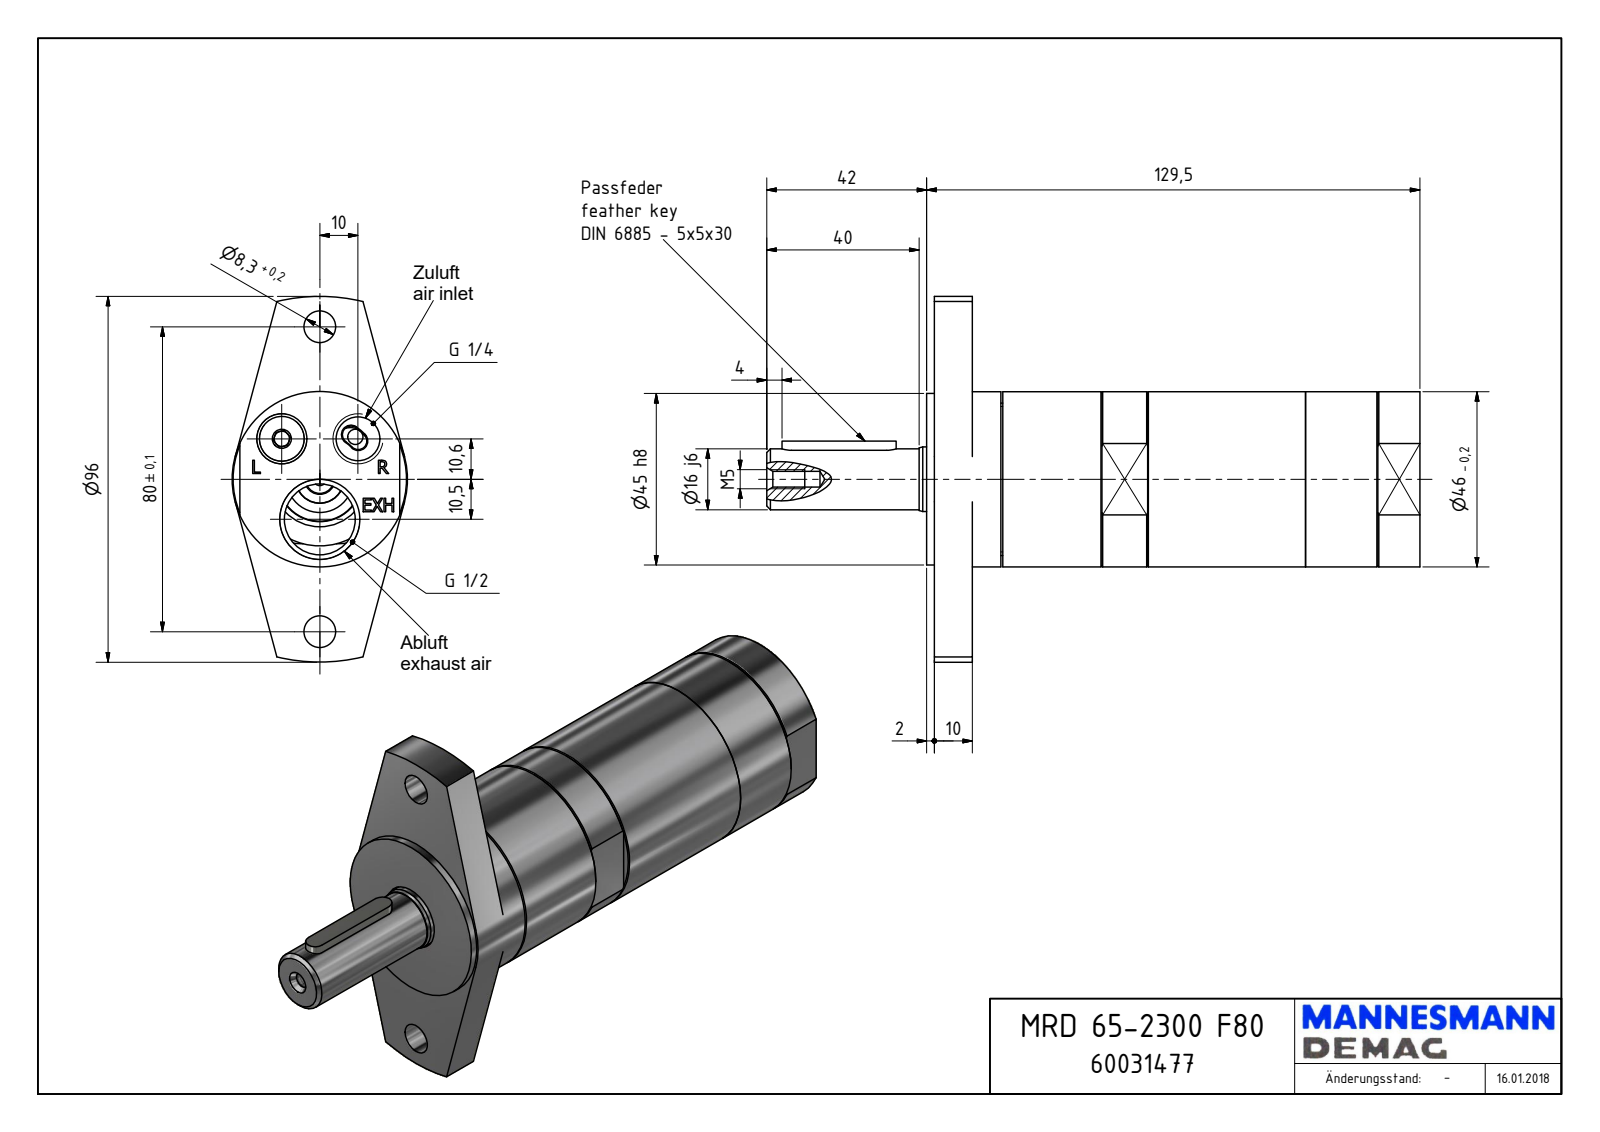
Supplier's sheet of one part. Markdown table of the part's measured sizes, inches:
| quantity | value |
| --- | --- |
| part name | MRD 65-2300 F80_60031477 |
| STEP written by | Autodesk Inventor 2018 (AUTOMOTIVE_DESIGN) |
| units | inches |
| bodies | 1 solid, 167 faces (109 planar, 32 cylindrical, 26 other) |
| overall size | 6.752 × 3.78 × 1.811 |
| volume | 14.32 in³ |
| surface area | 49.26 in² |
| round holes (diameter × count) | 0.327 × 2, 0.157 × 1, 0.163 × 1, 0.451 × 1, 0.689 × 1, 0.733 × 1 |
| round bosses / shafts (diameter × count) | 1.811 × 1, 1.772 × 1, 1.575 × 1, 1.403 × 1, 0.667 × 1, 0.63 × 1 |
| partial cylindrical surfaces (radius × count) | 0.098 × 2, 0.197 × 2, 0.225 × 1, 0.748 × 1, 1.89 × 1 |
| main face-to-face distances | 0.394, 0.472, 0.079, 4.626, 5.098, 5.02, 1.654, 1.811, 0.315, 4.311 |
| hole center spacings | 0.574, 0.919, 1.222, 1.575, 2.031, 0.413, 0.787, 1.161 |
